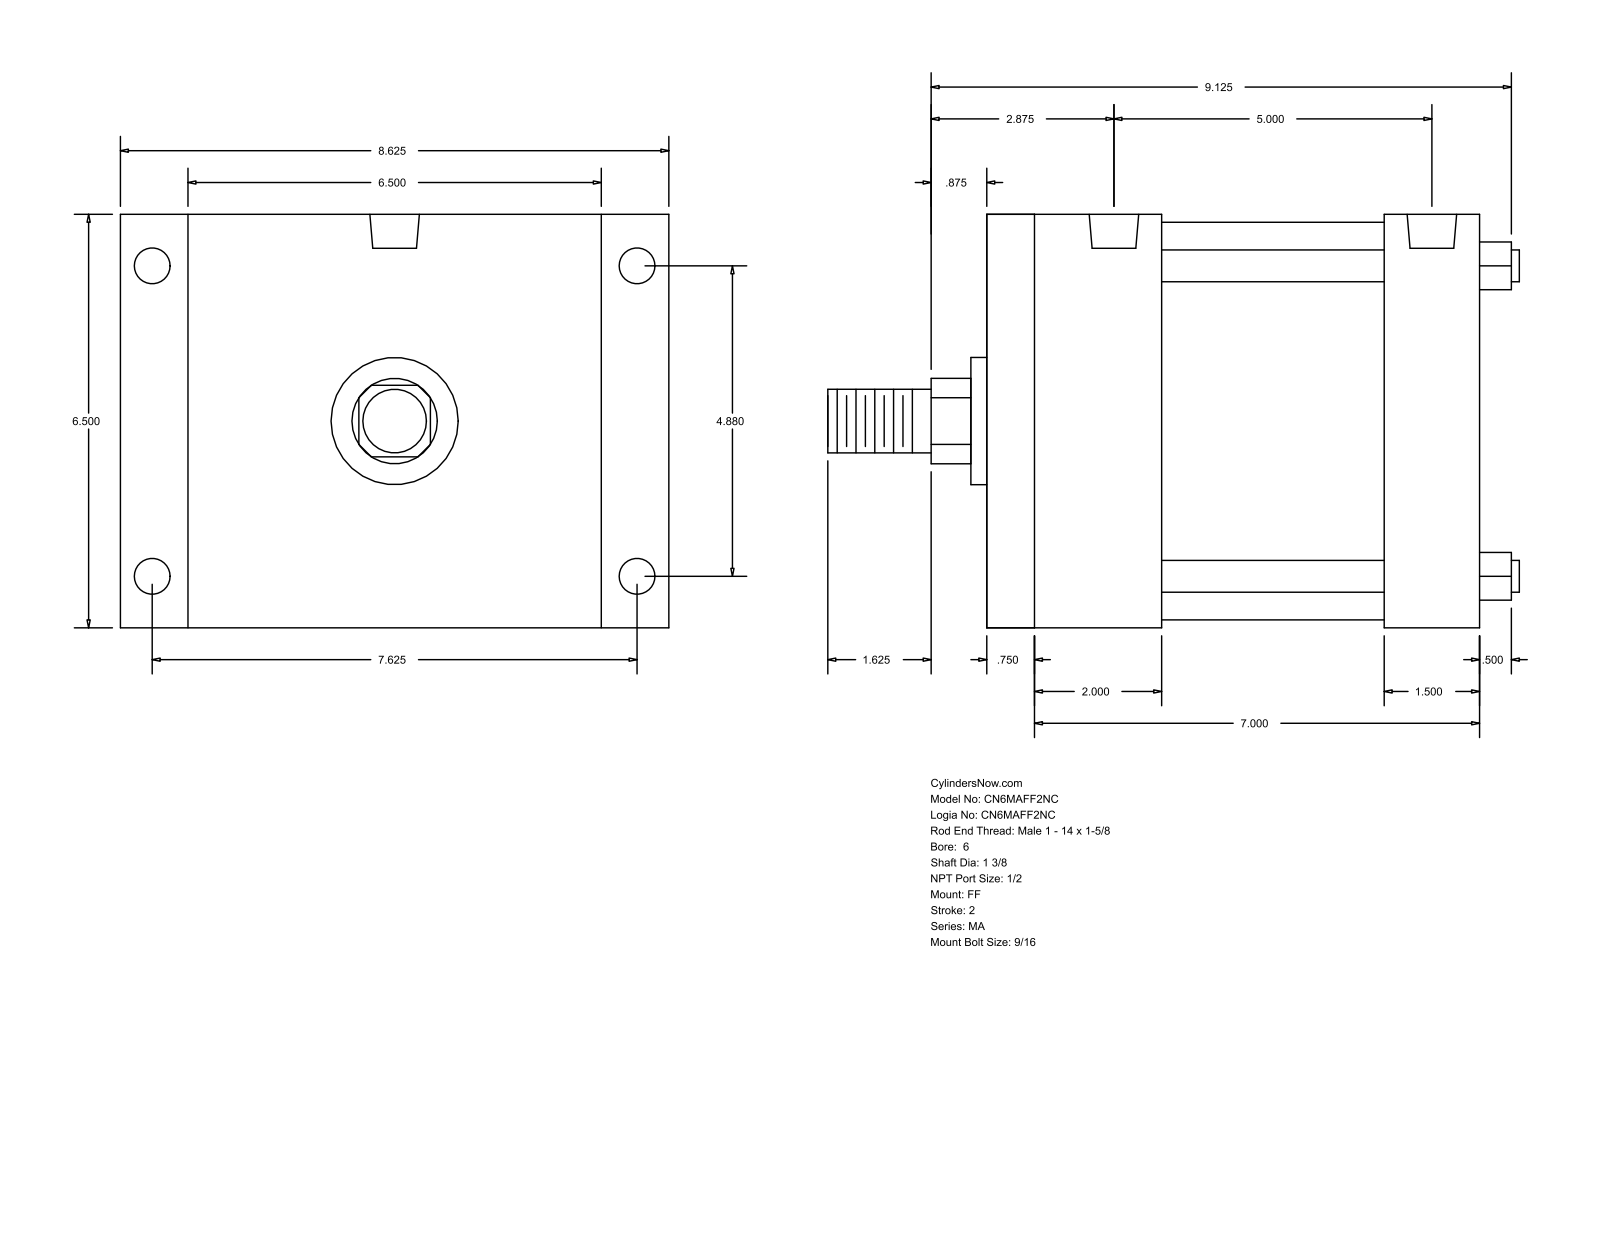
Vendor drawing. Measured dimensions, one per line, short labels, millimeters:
name: MA_FF__0600_1.375
written by: GSSL Pune (CONFIG_CONTROL_DESIGN)
unit: mm
bodies: 0 solids, 92 faces (64 planar, 28 cylindrical, 0 other)
size: 276.23 × 219.07 × 165.1
holes: 4× ⌀14.29, 4× ⌀17.46, 2× ⌀19.77
bosses: 4× ⌀12.7, 1× ⌀158.75, 1× ⌀50.8, 1× ⌀34.92, 1× ⌀25.4
rounds: 1× R17.06
face distances: 165.1, 196.84, 180.97, 15.87, 130.17, 38.1, 66.67, 50.8, 158.74, 142.87
hole spacings: 123.96, 130.18, 193.68, 229.95, 3.18, 127
